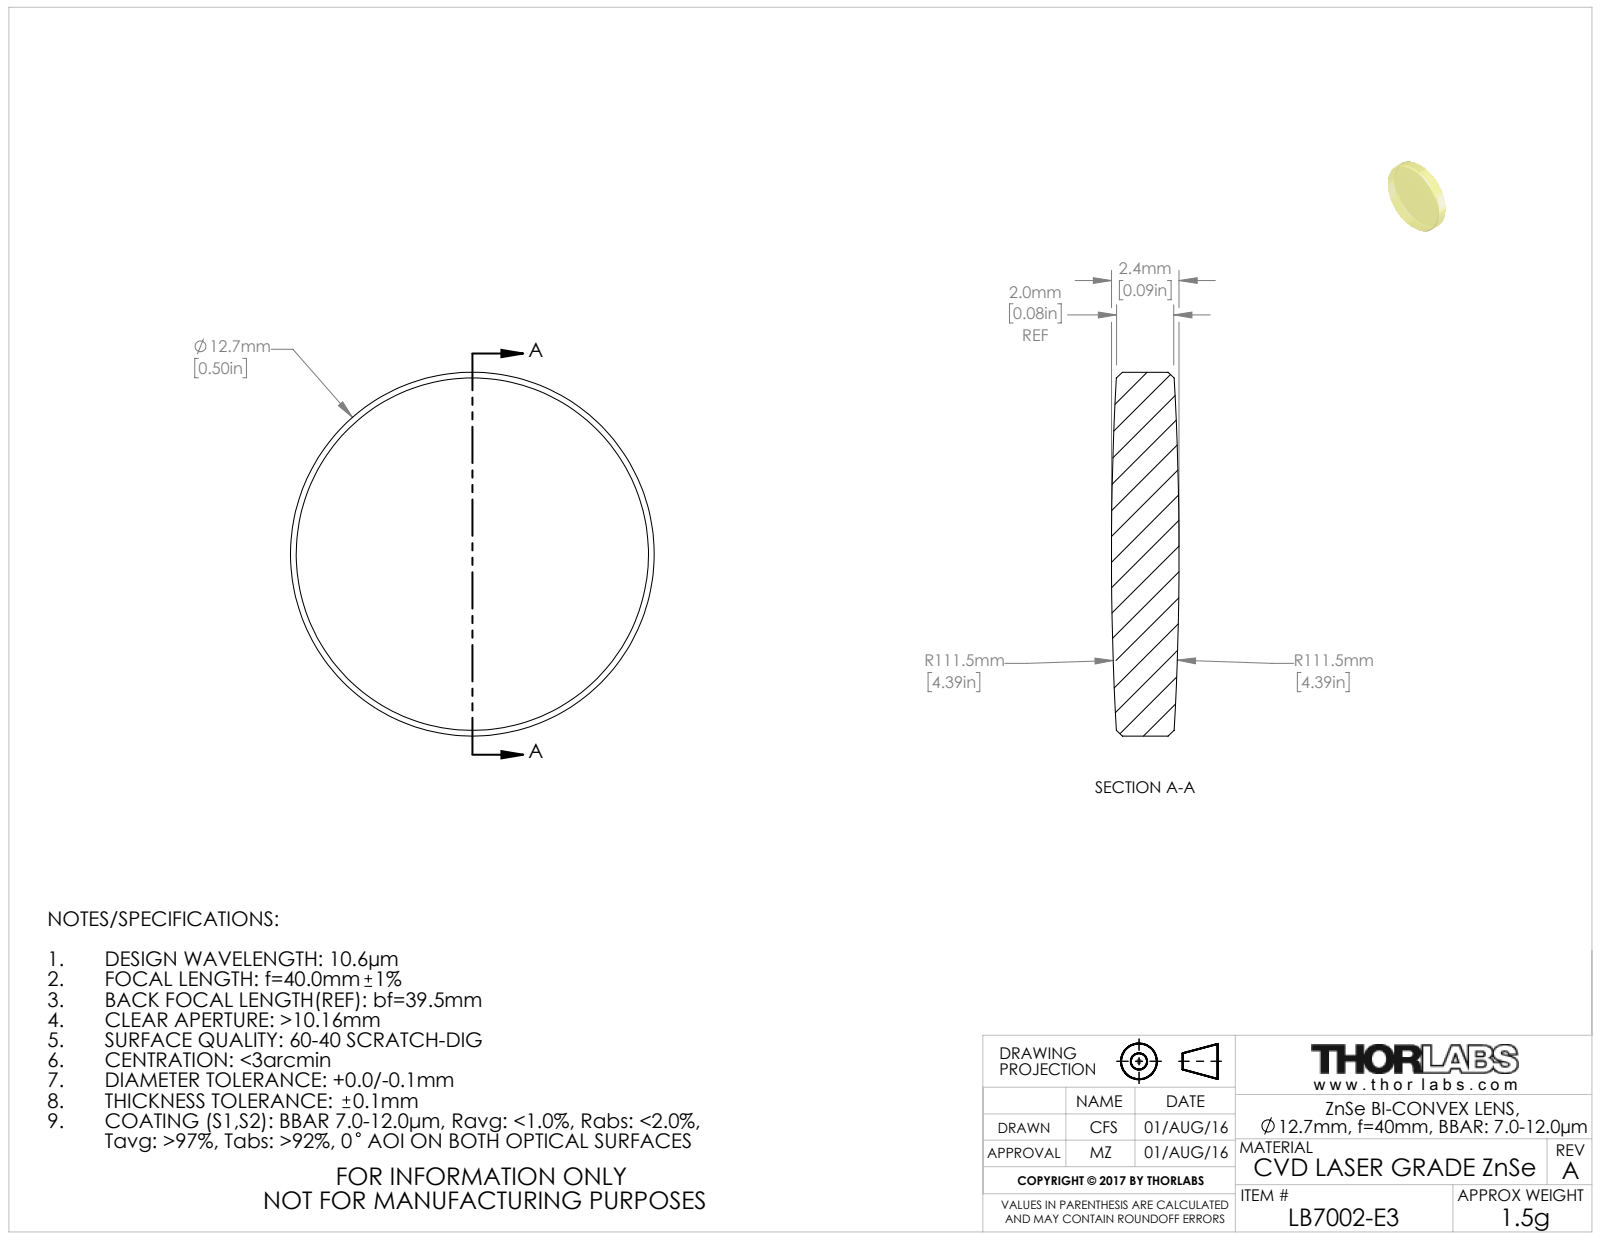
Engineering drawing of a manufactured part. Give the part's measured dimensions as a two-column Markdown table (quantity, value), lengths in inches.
| quantity | value |
| --- | --- |
| part name | TTN051881-E0W |
| STEP written by | SolidWorks 2016 (CONFIG_CONTROL_DESIGN) |
| units | inches |
| bodies | 1 solid, 10 faces (0 planar, 2 cylindrical, 8 other) |
| overall size | 0.5 × 0.5 × 0.093 |
| volume | 0.017 in³ |
| surface area | 0.503 in² |
| round bosses / shafts (diameter × count) | 0.5 × 1 |
